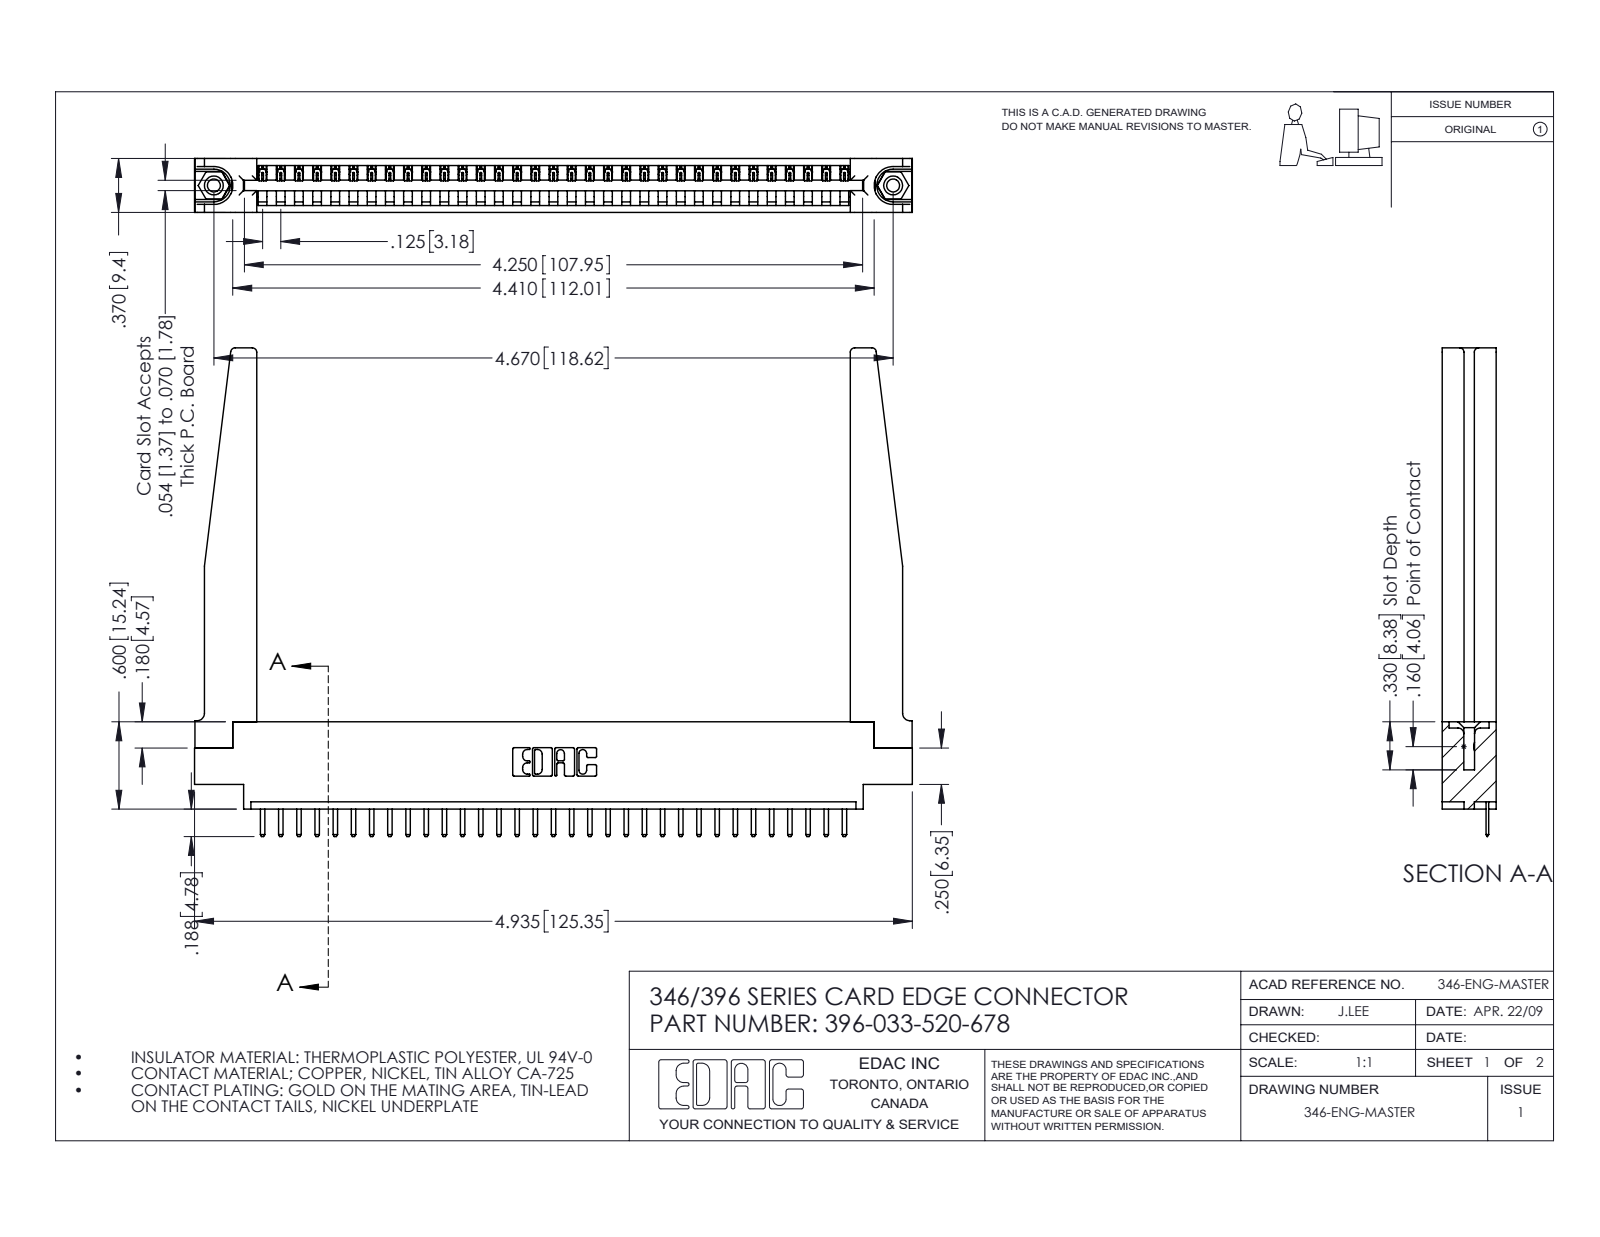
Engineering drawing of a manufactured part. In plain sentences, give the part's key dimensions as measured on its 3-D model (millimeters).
The part is named "396-033-520-678; 346-220-078_345-220-078; 346 Part_0.170 Offset - 0.156 Dia-TH; 345-250-001_345-250-001-102 (+1 more)". Its 3-D file was written by "SolidWorks 2016 (CONFIG_CONTROL_DESIGN)". It is 38 solids with 2406 faces: 1608 planar, 746 cylindrical and 52 other. Overall it measures 125.3 by 85.3 by 9.4 millimeters. Its volume is 18 600 cubic millimeters and its surface area 20 900 square millimeters. Round holes: 2 of diameter 2.3, 2 of diameter 3.2, 2 of diameter 4, 1 of diameter 1.6. Round bosses or shafts: 2 of diameter 3.9. Partial cylindrical surfaces (rounded edges, fillets, slot ends): 68 of radius 0.3, 66 of radius 0.2, 22 of radius 0.3, 8 of radius 0.8, 6 of radius 0.2, 6 of radius 0.8, 3 of radius 0.7, 2 of radius 0.8. The main face-to-face distances are 9.4, 1.2, 8.2, 3.8, 1.8, 3.8, 6.4, 5.6, 2.5, 4.4. The hole center spacings are 6.2, 113.3, 118.6.
